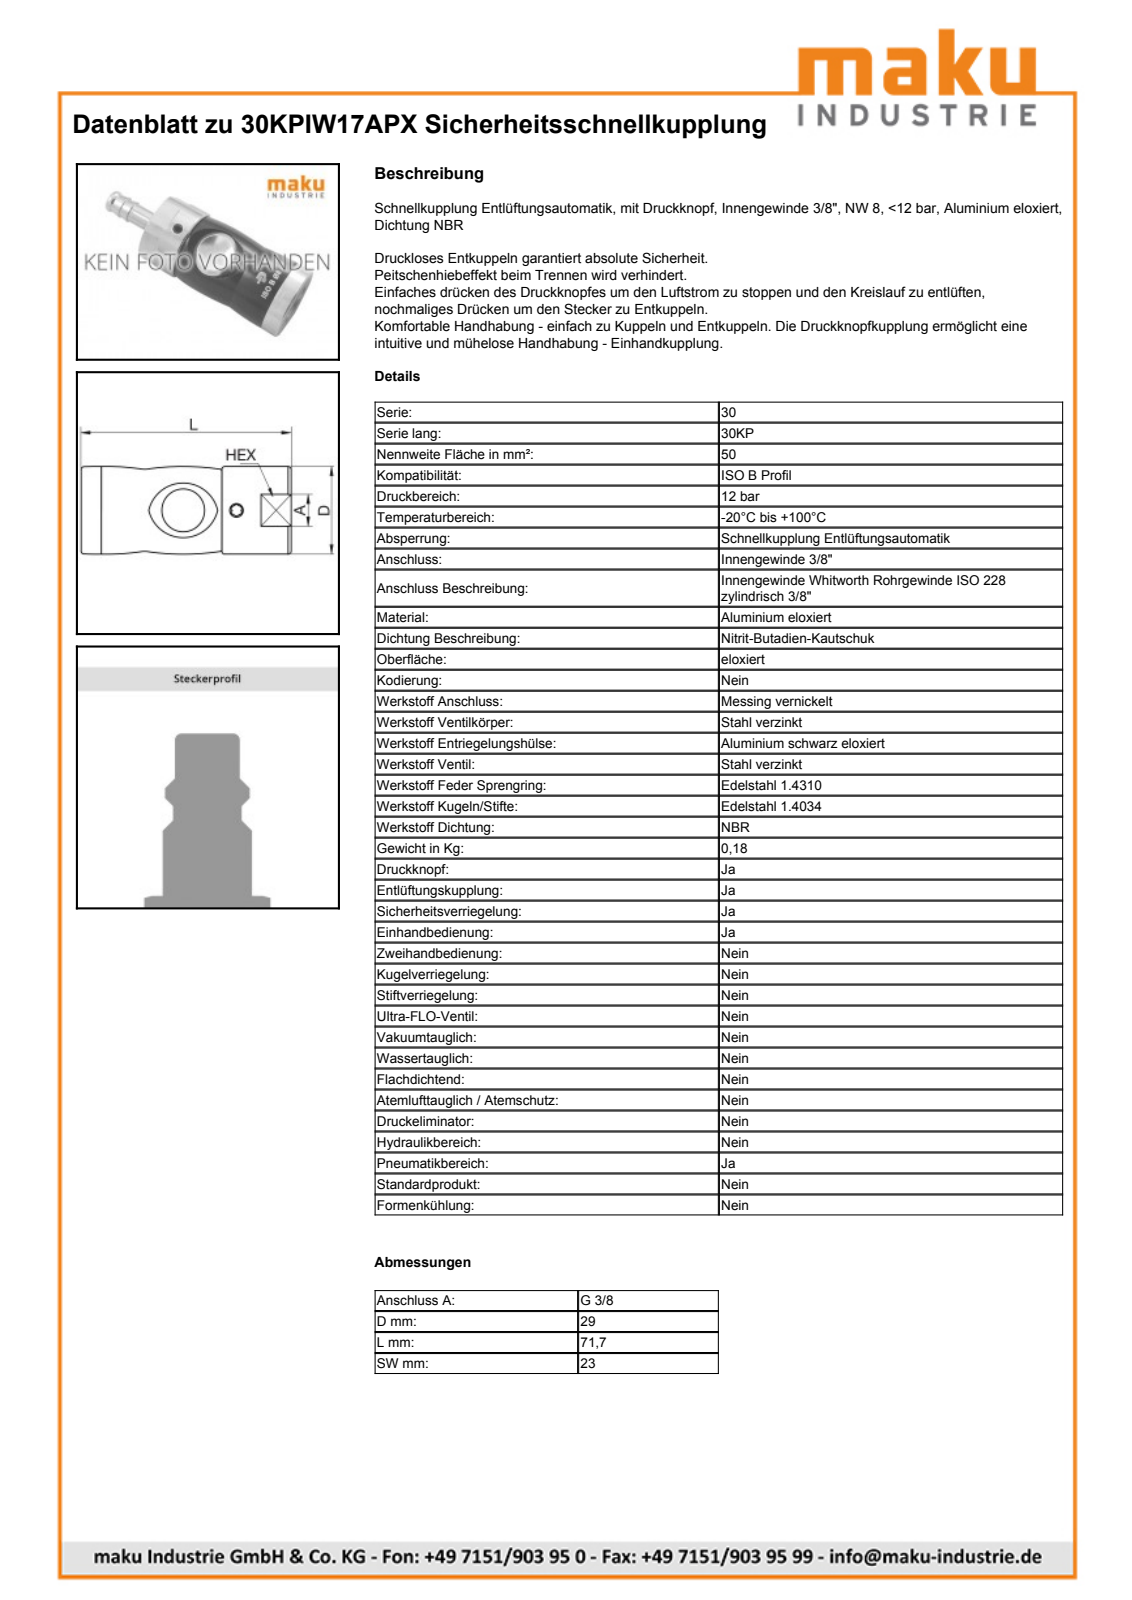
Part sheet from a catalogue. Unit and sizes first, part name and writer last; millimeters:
Units: millimetres
Overall size (bounding box): 71.7 × 29.04 × 29.04
Round holes (diameter × count): ⌀3.5 ×1, ⌀8 ×1, ⌀8.5 ×1, ⌀11.1 ×1, ⌀11.2 ×1, ⌀12.2 ×1, ⌀13.6 ×1, ⌀14 ×1, ⌀14.59 ×1, ⌀16 ×1, ⌀17.5 ×1, ⌀18.1 ×1
Round bosses / shafts (diameter × count): ⌀29 ×1, ⌀26 ×1, ⌀24.5 ×1, ⌀24.23 ×1, ⌀20.5 ×1, ⌀18.65 ×1, ⌀18.2 ×1, ⌀18 ×1
Partial cylindrical surfaces — rounded edges, fillets, slot ends (radius × count): R2.5 ×4, R7.1 ×2, R5.2 ×1
Main face-to-face distances: 46.7, 6.7, 40, 25, 65, 71.7, 12.26, 12.74, 52.74, 59.44
Hole centre spacings: 17.65
Volume: 50 018 mm³ · Surface area: 29 449 mm²
Bodies: 44 solids, 276 faces (80 planar, 89 cylindrical, 107 other)
Part name (STEP PRODUCT): 30KPIW17APX
STEP written by: Autodesk Inventor 2019 (CONFIG_CONTROL_DESIGN)
